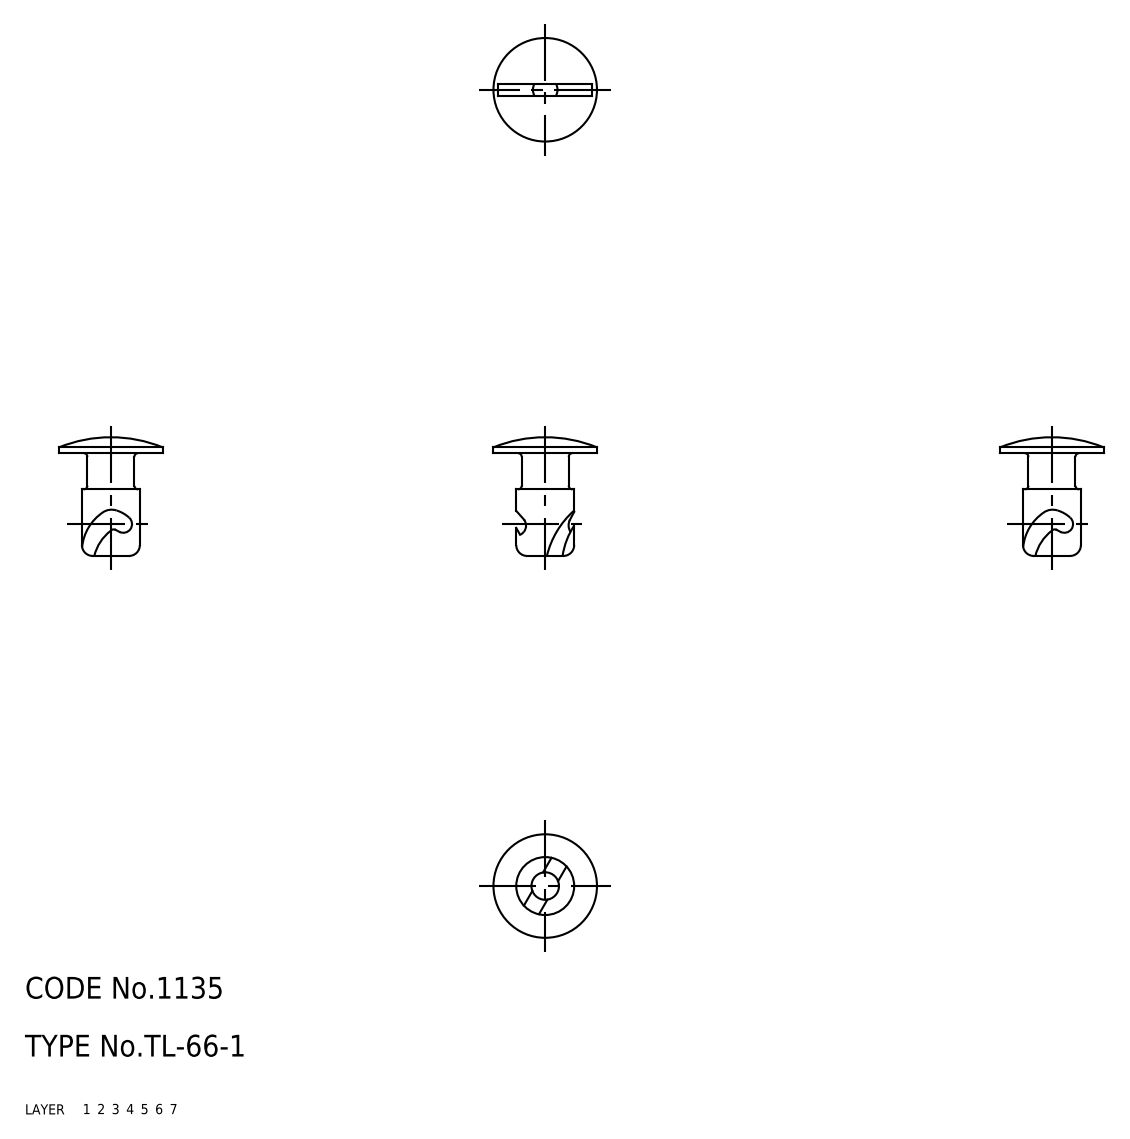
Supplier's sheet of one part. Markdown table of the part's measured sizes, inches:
| quantity | value |
| --- | --- |
| part name | fastener; TL_66_1 |
| STEP written by | SolidWorks 2015 (AUTOMOTIVE_DESIGN) |
| units | inches |
| bodies | 1 solid, 47 faces (12 planar, 20 cylindrical, 15 other) |
| overall size | 0.645 × 0.563 × 0.563 |
| volume | 0.036 in³ |
| surface area | 1.37 in² |
| round holes (diameter × count) | 0.15 × 1 |
| round bosses / shafts (diameter × count) | 0.563 × 1, 0.315 × 1, 0.256 × 1 |
| partial cylindrical surfaces (radius × count) | 0.047 × 2, 0.116 × 2, 0.21 × 2 |
| main face-to-face distances | 0.041, 0.067, 0.197, 0.238, 0.362, 0.559, 0.6 |
